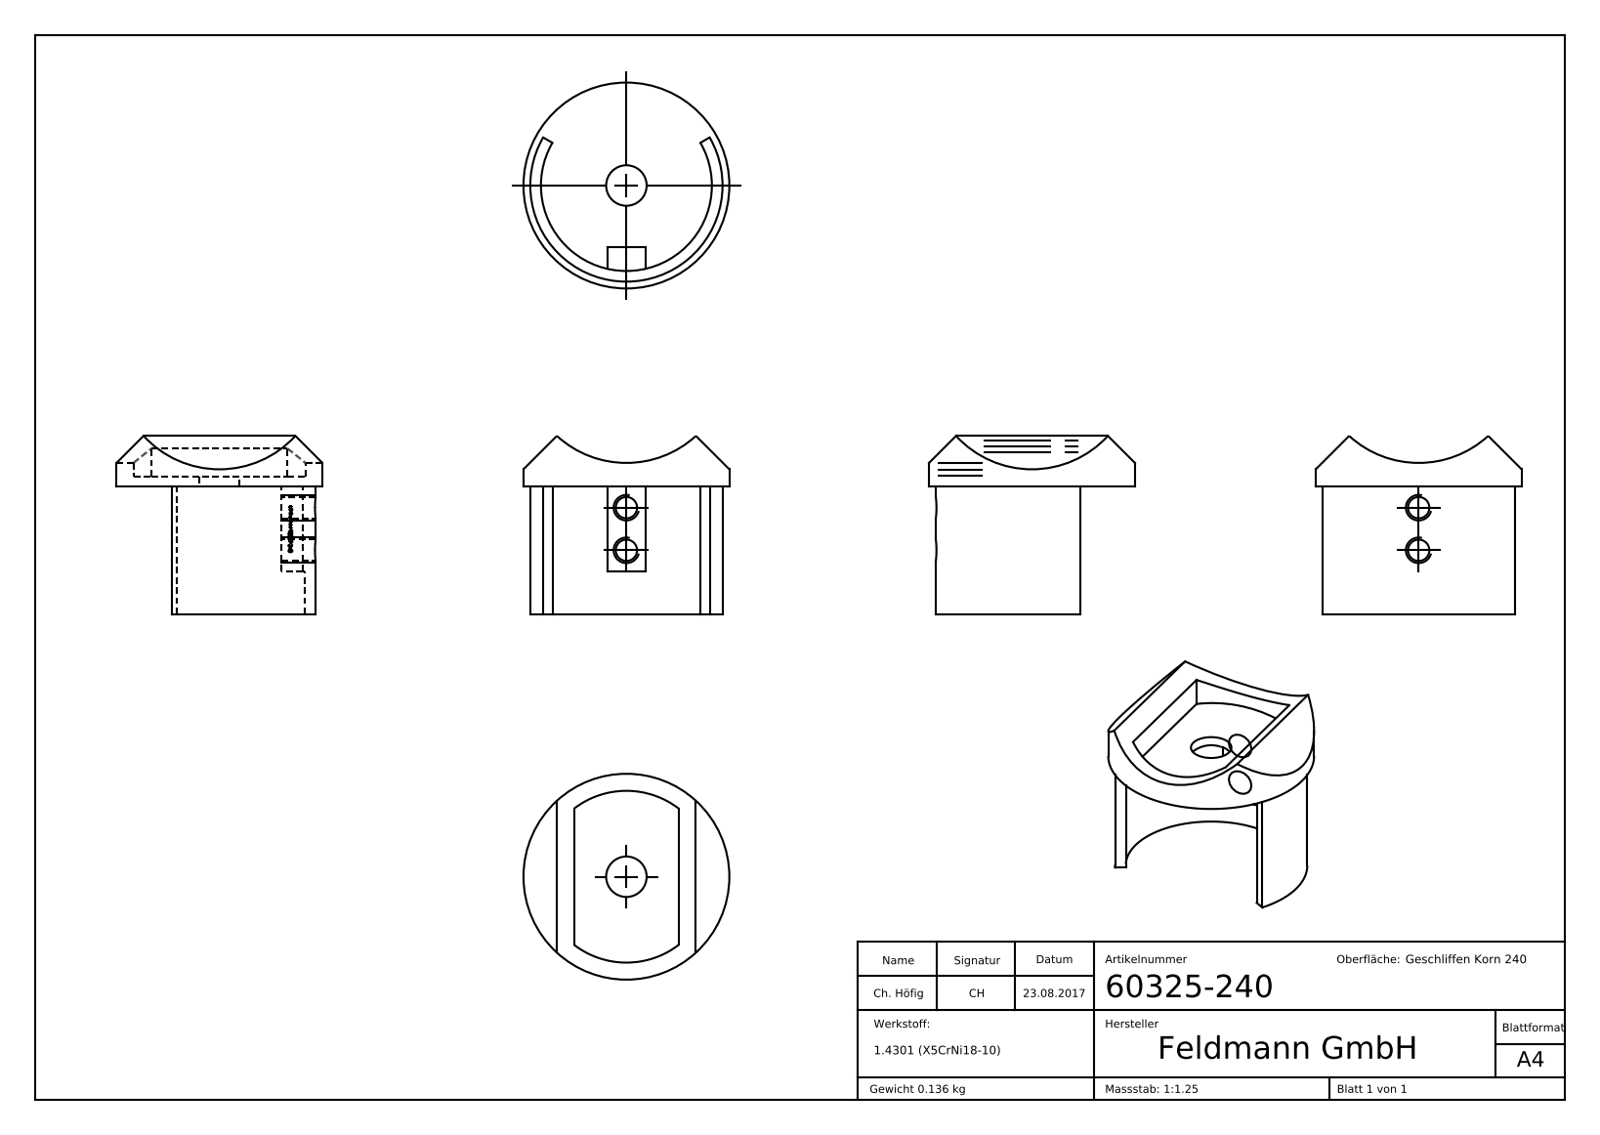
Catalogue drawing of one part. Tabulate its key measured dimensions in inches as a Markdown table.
| quantity | value |
| --- | --- |
| part name | 60325-240 |
| STEP written by | SolidWorks 2015 (CONFIG_CONTROL_DESIGN) |
| units | inches |
| bodies | 1 solid, 255 faces (132 planar, 14 cylindrical, 109 other) |
| overall size | 1.902 × 1.902 × 1.647 |
| volume | 1.05 in³ |
| surface area | 17.75 in² |
| round holes (diameter × count) | 0.197 × 2, 0.374 × 1 |
| round bosses / shafts (diameter × count) | 1.902 × 1 |
| partial cylindrical surfaces (radius × count) | 0.789 × 1, 0.793 × 1, 0.888 × 1, 0.951 × 1 |
| main face-to-face distances | 0.091, 1.181, 1.272, 0.969, 0.307, 0.662, 0.354, 0.394, 0.787, 0.878 |
| hole center spacings | 0.394 |
